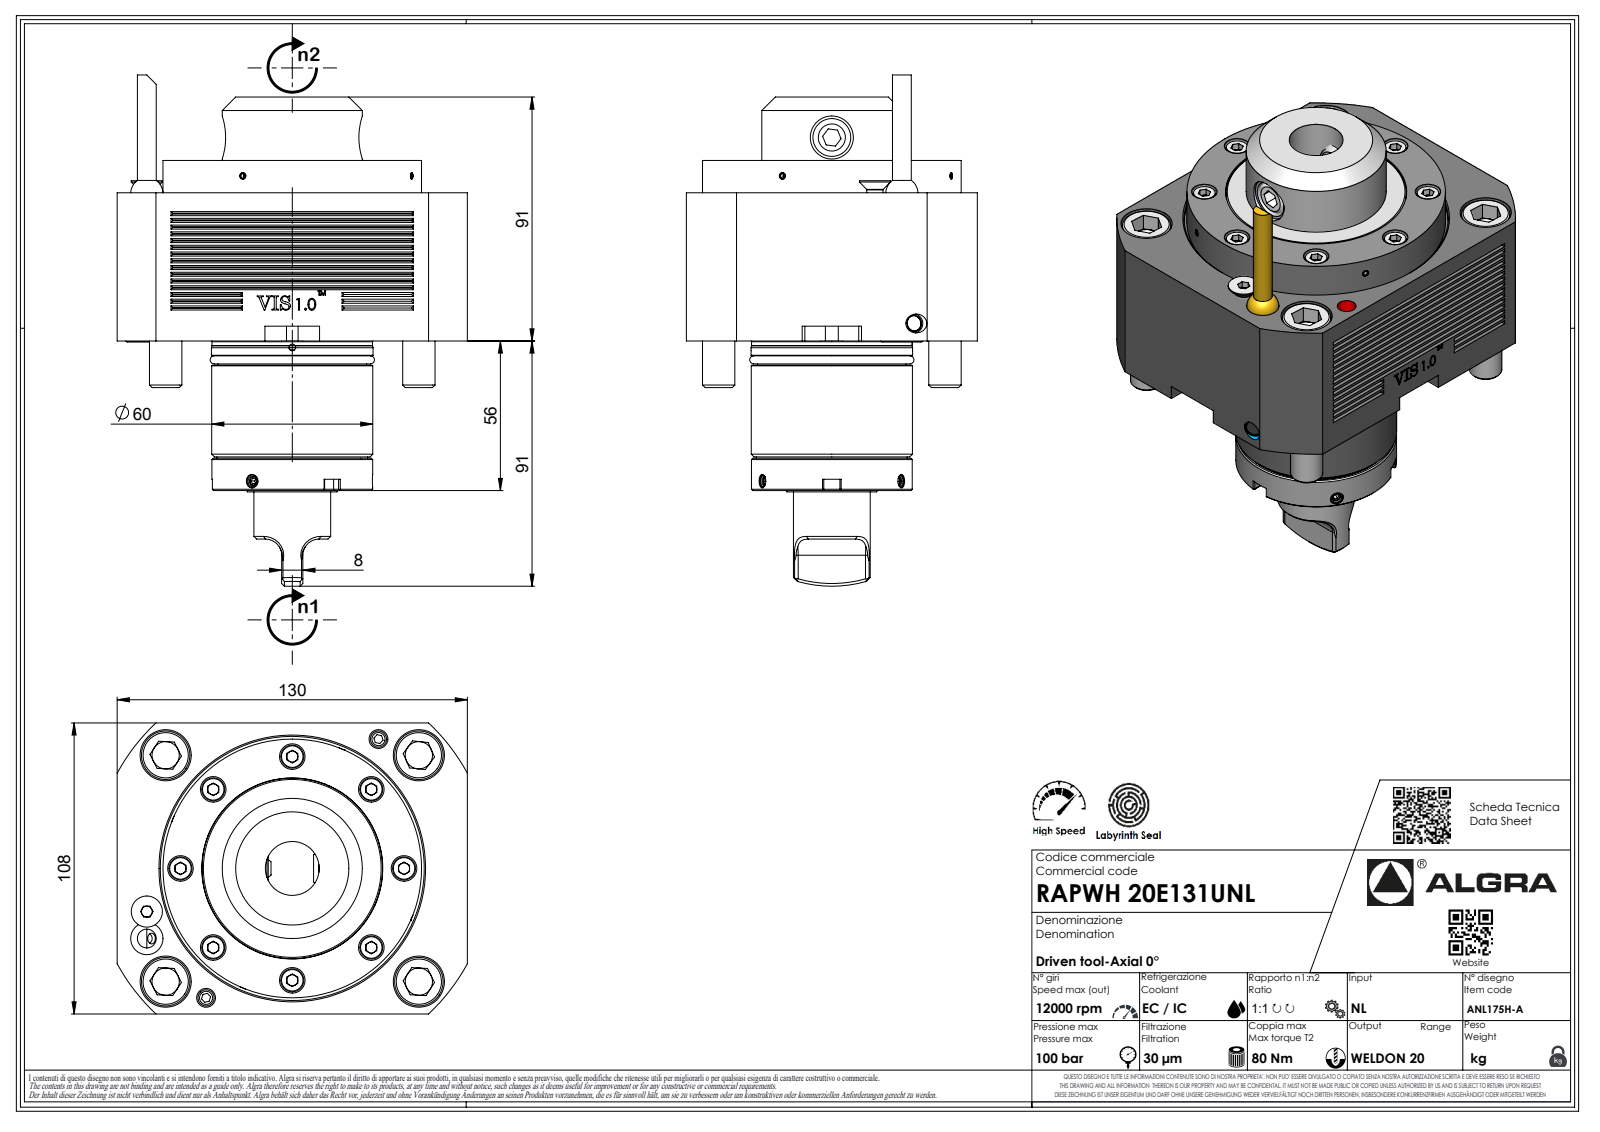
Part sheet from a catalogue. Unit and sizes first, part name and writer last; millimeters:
Units: millimetres
Overall size (bounding box): 189.7 × 130 × 108
Round holes (diameter × count): ⌀2.1 ×1, ⌀4 ×1
Round bosses / shafts (diameter × count): ⌀12 ×4, ⌀96 ×1, ⌀60 ×1, ⌀59.8 ×1, ⌀52 ×1, ⌀28.5 ×1, ⌀7 ×1, ⌀6.37 ×1
Partial cylindrical surfaces — rounded edges, fillets, slot ends (radius × count): R8 ×8, R0.33 ×7, R0.52 ×7, R3.7 ×7, R6 ×6, R0.21 ×1, R2 ×1, R46 ×1
Main face-to-face distances: 55, 108, 67, 12, 130, 55.5, 110.5, 122.5, 61.5, 61
Volume: 1 053 000 mm³ · Surface area: 75 571 mm²
Bodies: 1 solid, 401 faces (260 planar, 58 cylindrical, 83 other)
Part name (STEP PRODUCT): RAPWH20E131UNL
STEP written by: SolidWorks 2023 (AUTOMOTIVE_DESIGN)
